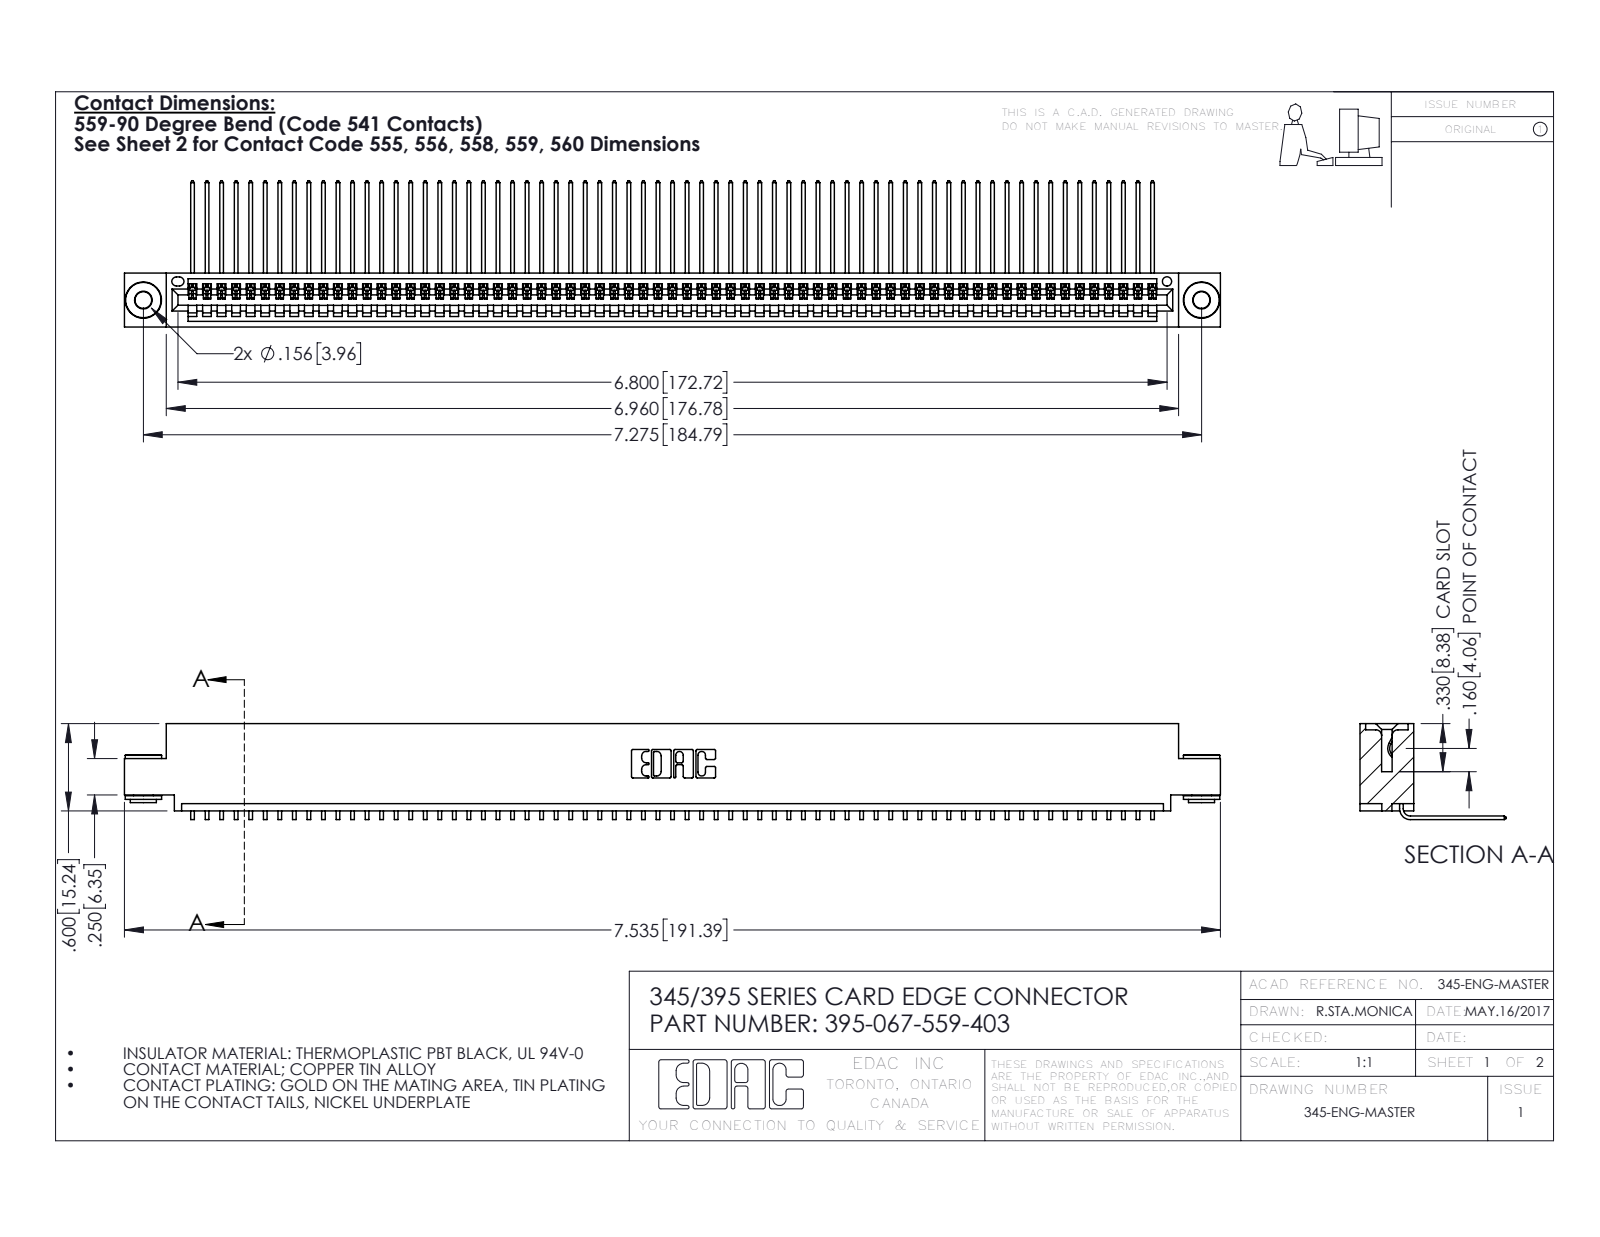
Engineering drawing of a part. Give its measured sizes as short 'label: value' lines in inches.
name: 345 Part_0.110 Offset - 0.156 Dia-TH; 345-292-001_558 559 Tail - 1; 345-250-002_345-250-002-102; 395-067-559-403
written by: SolidWorks 2016 (CONFIG_CONTROL_DESIGN)
unit: in
bodies: 70 solids, 4188 faces (2908 planar, 1272 cylindrical, 8 other)
size: 7.535 × 1.005 × 0.659
volume: 1.132 in³; area: 41.23 in²
holes: 2× ⌀0.116, 2× ⌀0.156, 1× ⌀0.064
bosses: 2× ⌀0.25, 2× ⌀0.18, 2× ⌀0.136
rounds: 134× R0.006, 22× R0.01, 6× R0.007, 6× R0.031, 3× R0.026, 2× R0.031, 2× R0.04, 1× R0.014
face distances: 0.072, 0.298, 0.37, 0.2, 0.025, 0.098, 0.272, 0.225, 0.149, 0.072
hole spacings: 0.27, 7.039, 7.275
